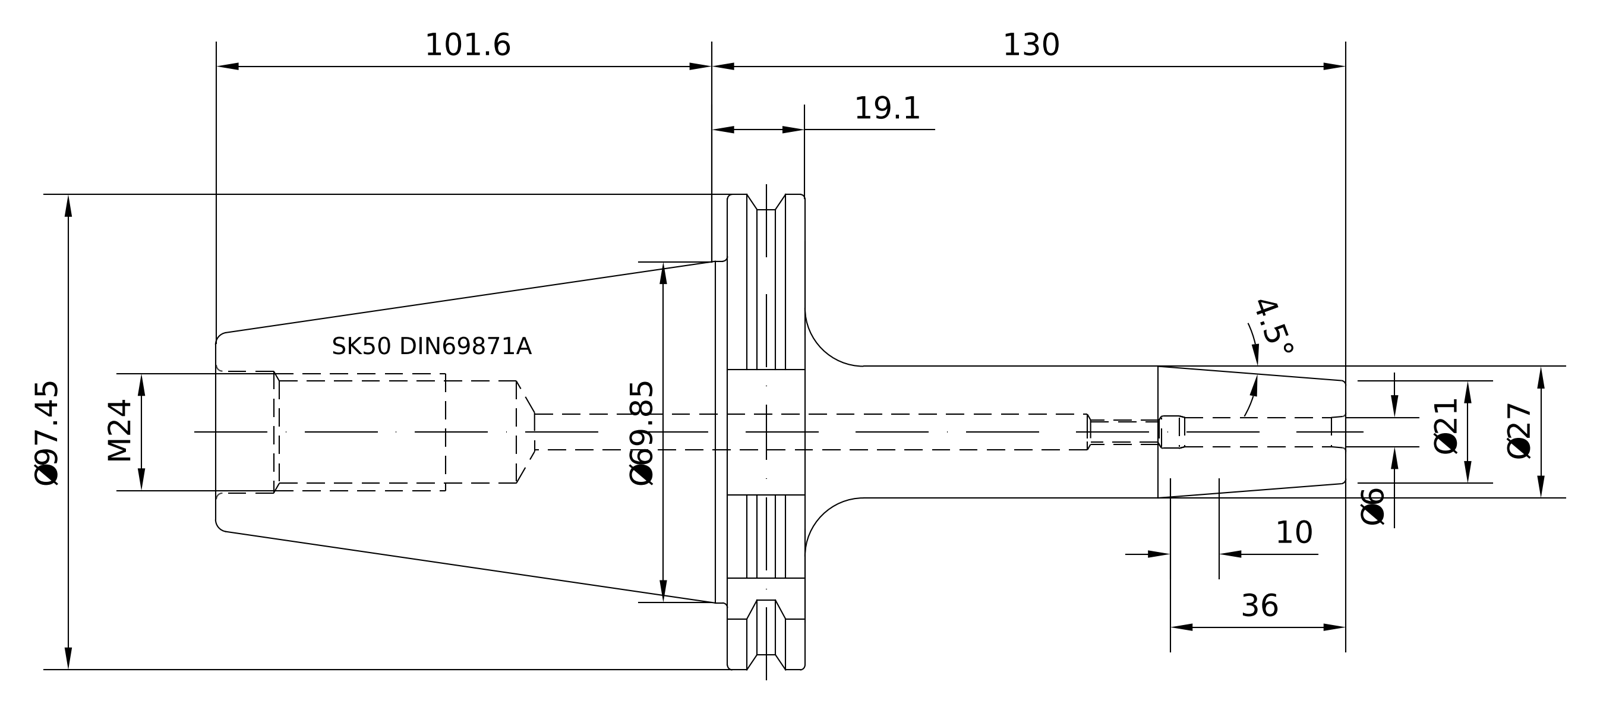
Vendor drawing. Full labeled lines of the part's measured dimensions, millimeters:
Part name (STEP PRODUCT): 50-444-06
STEP written by: PRO/ENGINEER BY PARAMETRIC TECHNOLOGY CORPORATION, 2010430 (CONFIG_CONTROL_DESIGN)
Units: millimetres
Bodies: 1 solid, 93 faces (21 planar, 24 cylindrical, 48 other)
Overall size (bounding box): 231.6 × 97.47 × 94
Volume: 400 481 mm³ · Surface area: 51 759 mm²
Round holes (diameter × count): ⌀6 ×1, ⌀20.75 ×1, ⌀25.01 ×1, ⌀25.7 ×1
Round bosses / shafts (diameter × count): ⌀91 ×1, ⌀69.15 ×1, ⌀27 ×1, ⌀24.01 ×1
Partial cylindrical surfaces — rounded edges, fillets, slot ends (radius × count): R1.75 ×1, R48.74 ×1
Main face-to-face distances: 15.85, 72.8, 104.8, 120.65, 25.8, 231.6, 126.8, 110.95, 48, 56.8
